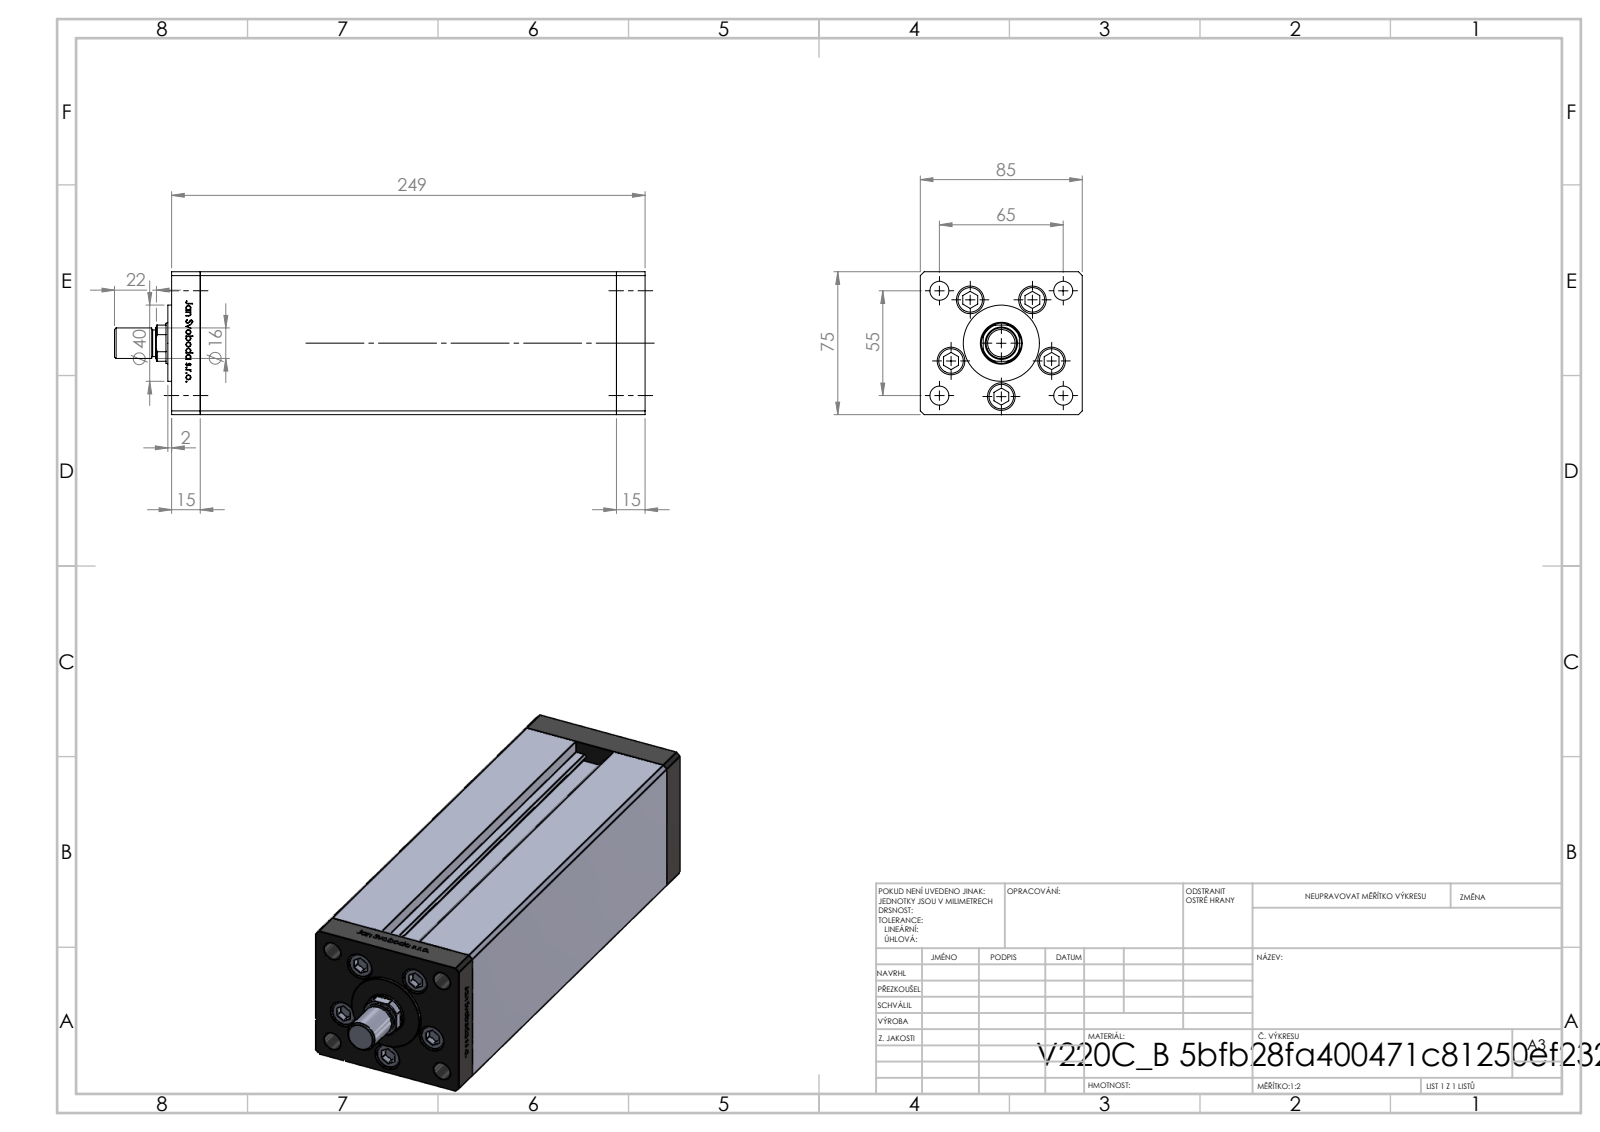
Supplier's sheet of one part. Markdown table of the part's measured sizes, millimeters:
| quantity | value |
| --- | --- |
| part name | ALLEN BOLT; V220C_B MIDDLE; V220C_FRONT_B; V220C_B_VC (+2 more) |
| STEP written by | SolidWorks 2019 (CONFIG_CONTROL_DESIGN) |
| units | millimeters |
| bodies | 15 solids, 1191 faces (466 planar, 147 cylindrical, 578 other) |
| overall size | 278.5 × 85 × 75 |
| volume | 1 385 000 mm³ |
| surface area | 197 194 mm² |
| round holes (diameter × count) | 11 × 5, 14.5 × 5, 10 × 4, 2 × 2, 13.16 × 2, 15 × 1, 22 × 1 |
| round bosses / shafts (diameter × count) | 8 × 5, 40 × 1, 16 × 1, 14 × 1 |
| partial cylindrical surfaces (radius × count) | 0.93 × 2, 10.5 × 1 |
| main face-to-face distances | 85, 75, 218.5, 15, 233.5, 248.5, 68.5, 64.5, 10.5, 31.25 |
| hole center spacings | 28, 42.57, 16.86, 19.17, 32.33, 32.5, 33.63, 37.33 |
